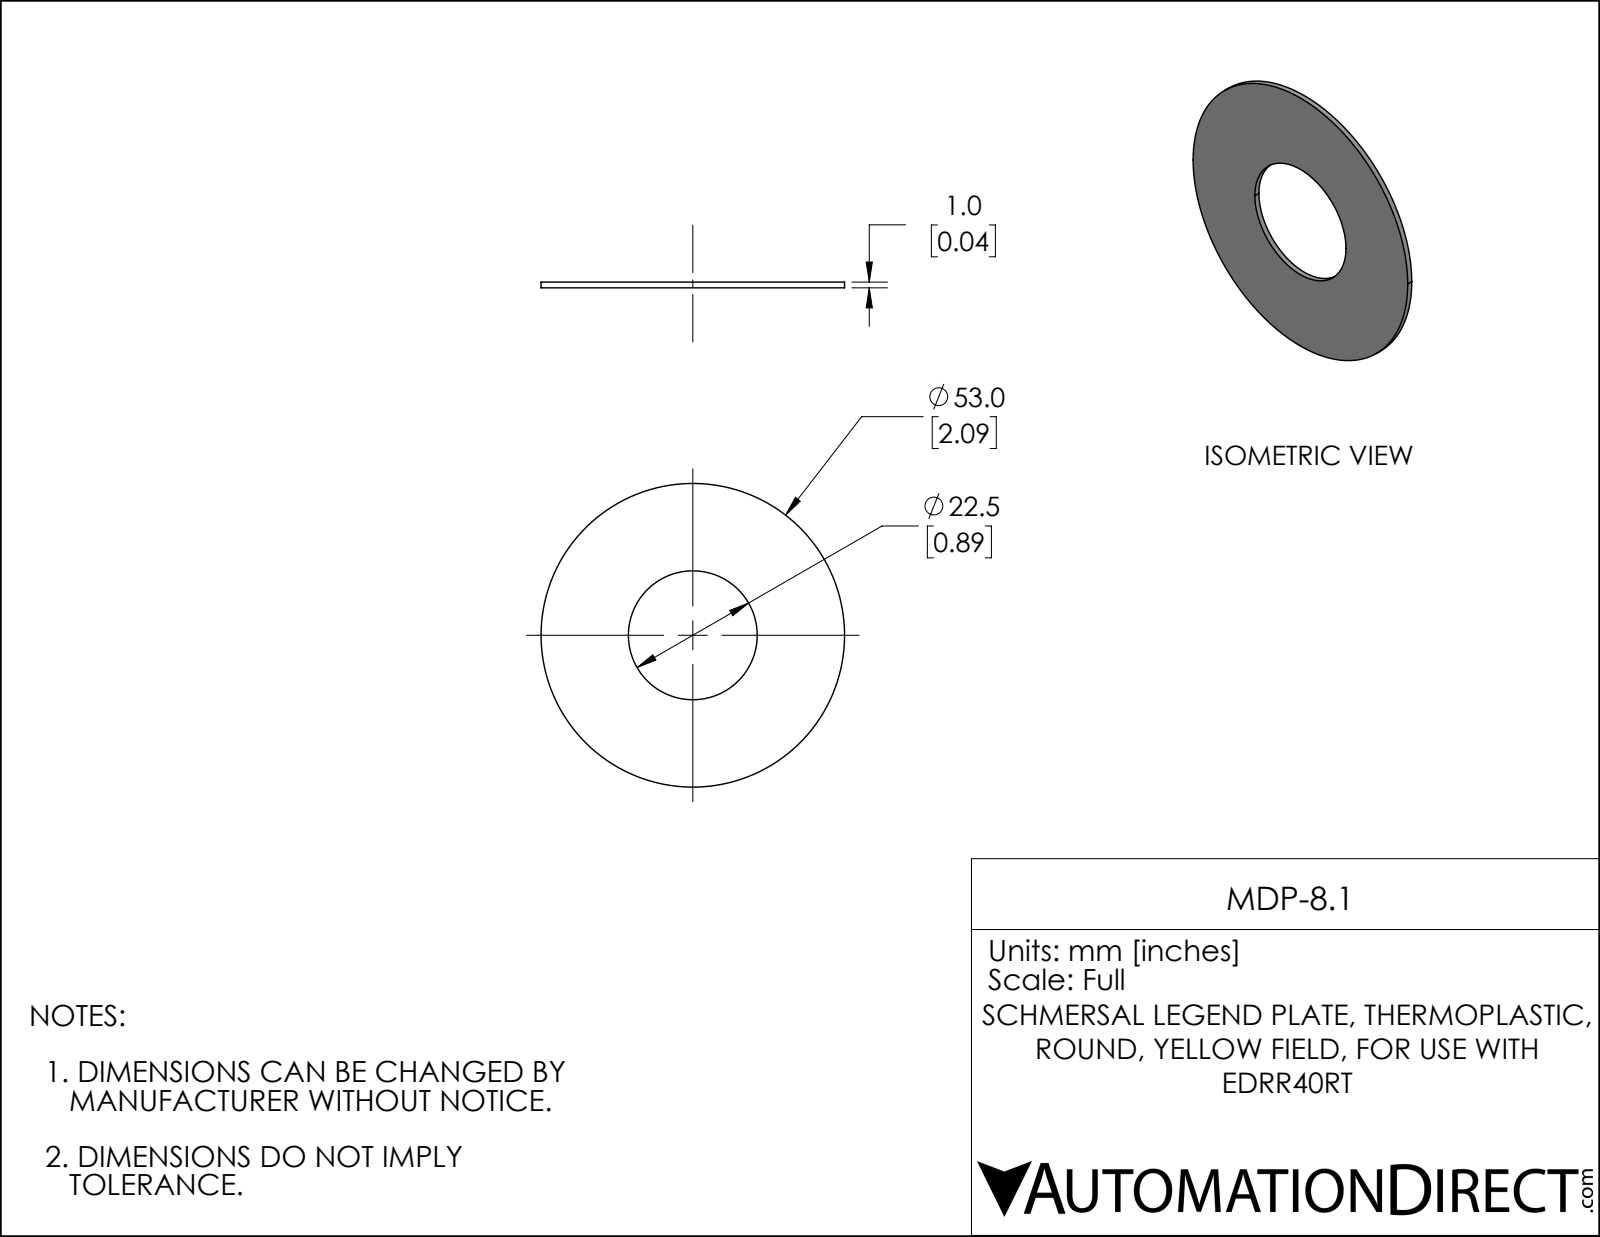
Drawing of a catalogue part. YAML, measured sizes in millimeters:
part_name: "MDP-8_1"
step_written_by: "CREO PARAMETRIC BY PTC INC, 2019444 (CONFIG_CONTROL_DESIGN)"
units: millimeters
bodies: {solids: 1, faces: 6, planar: 2, cylindrical: 4, other: 0}
overall_size: [53, 53, 1]
volume: 1809
surface_area: 3854
round_holes:
  - {diameter: 22.5, count: 1}
round_bosses_or_shafts:
  - {diameter: 53, count: 1}
face_to_face_distances: [1]
